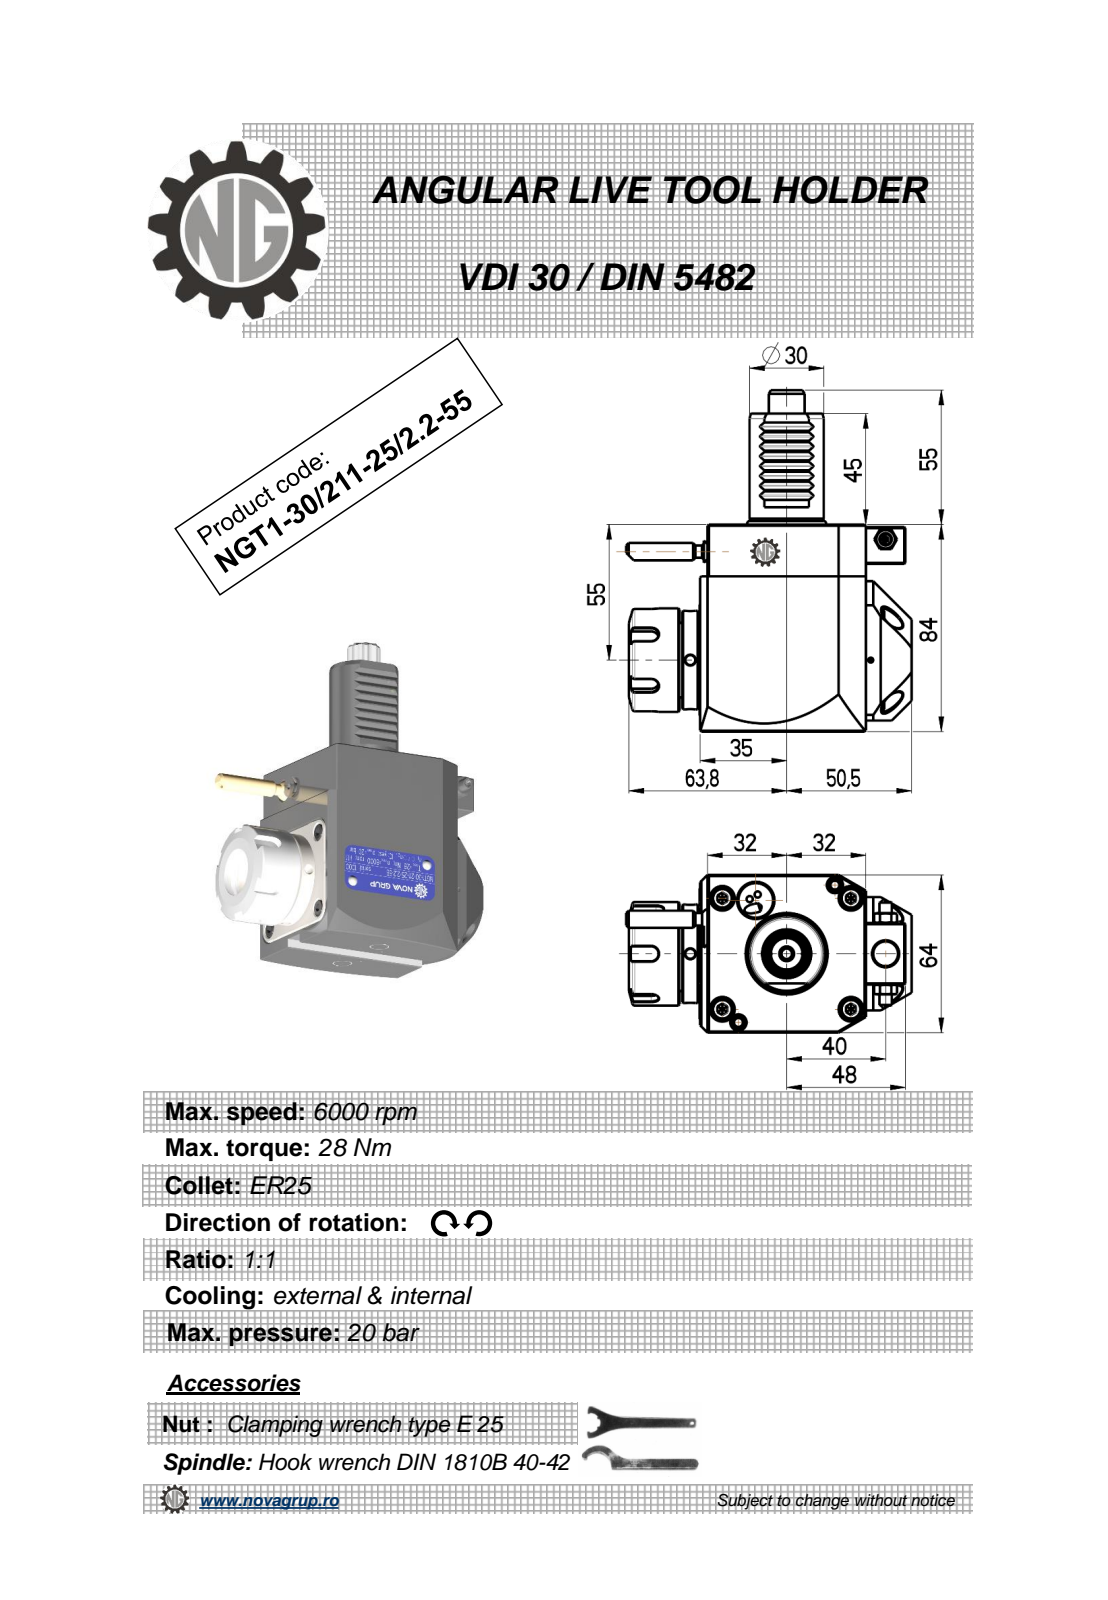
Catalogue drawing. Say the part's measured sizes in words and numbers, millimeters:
The part is named "NGT1_30_211_25_2_2_55". Its 3-D file was written by "PRO/ENGINEER BY PARAMETRIC TECHNOLOGY CORPORATION, 2010280 (CONFIG_CONTROL_DESIGN)". It is 1 solid with 439 faces: 172 planar, 114 cylindrical and 153 other. Overall it measures 139 by 115.38 by 65.6 millimeters. Its volume is 451 239 cubic millimeters and its surface area 45 783 square millimeters. Round holes: 2 of diameter 4, 2 of diameter 4.2, 1 of diameter 2.5, 1 of diameter 3, 1 of diameter 9.5, 1 of diameter 10, 1 of diameter 20.3. Round bosses or shafts: 2 of diameter 8.96, 2 of diameter 5, 1 of diameter 42, 1 of diameter 40, 1 of diameter 33, 1 of diameter 30, 1 of diameter 7. Partial cylindrical surfaces (rounded edges, fillets, slot ends): 16 of radius 2.91, 12 of radius 0.26, 8 of radius 0.3, 5 of radius 3, 2 of radius 160, 1 of radius 5.7, 1 of radius 7.25, 1 of radius 32. The main face-to-face distances are 64, 84, 67.2, 3.2, 3, 67, 80, 0.5, 85.7, 85.5. The hole center spacings are 14.22, 38.95, 40, 46.17, 46.5, 78.95, 92.92.
